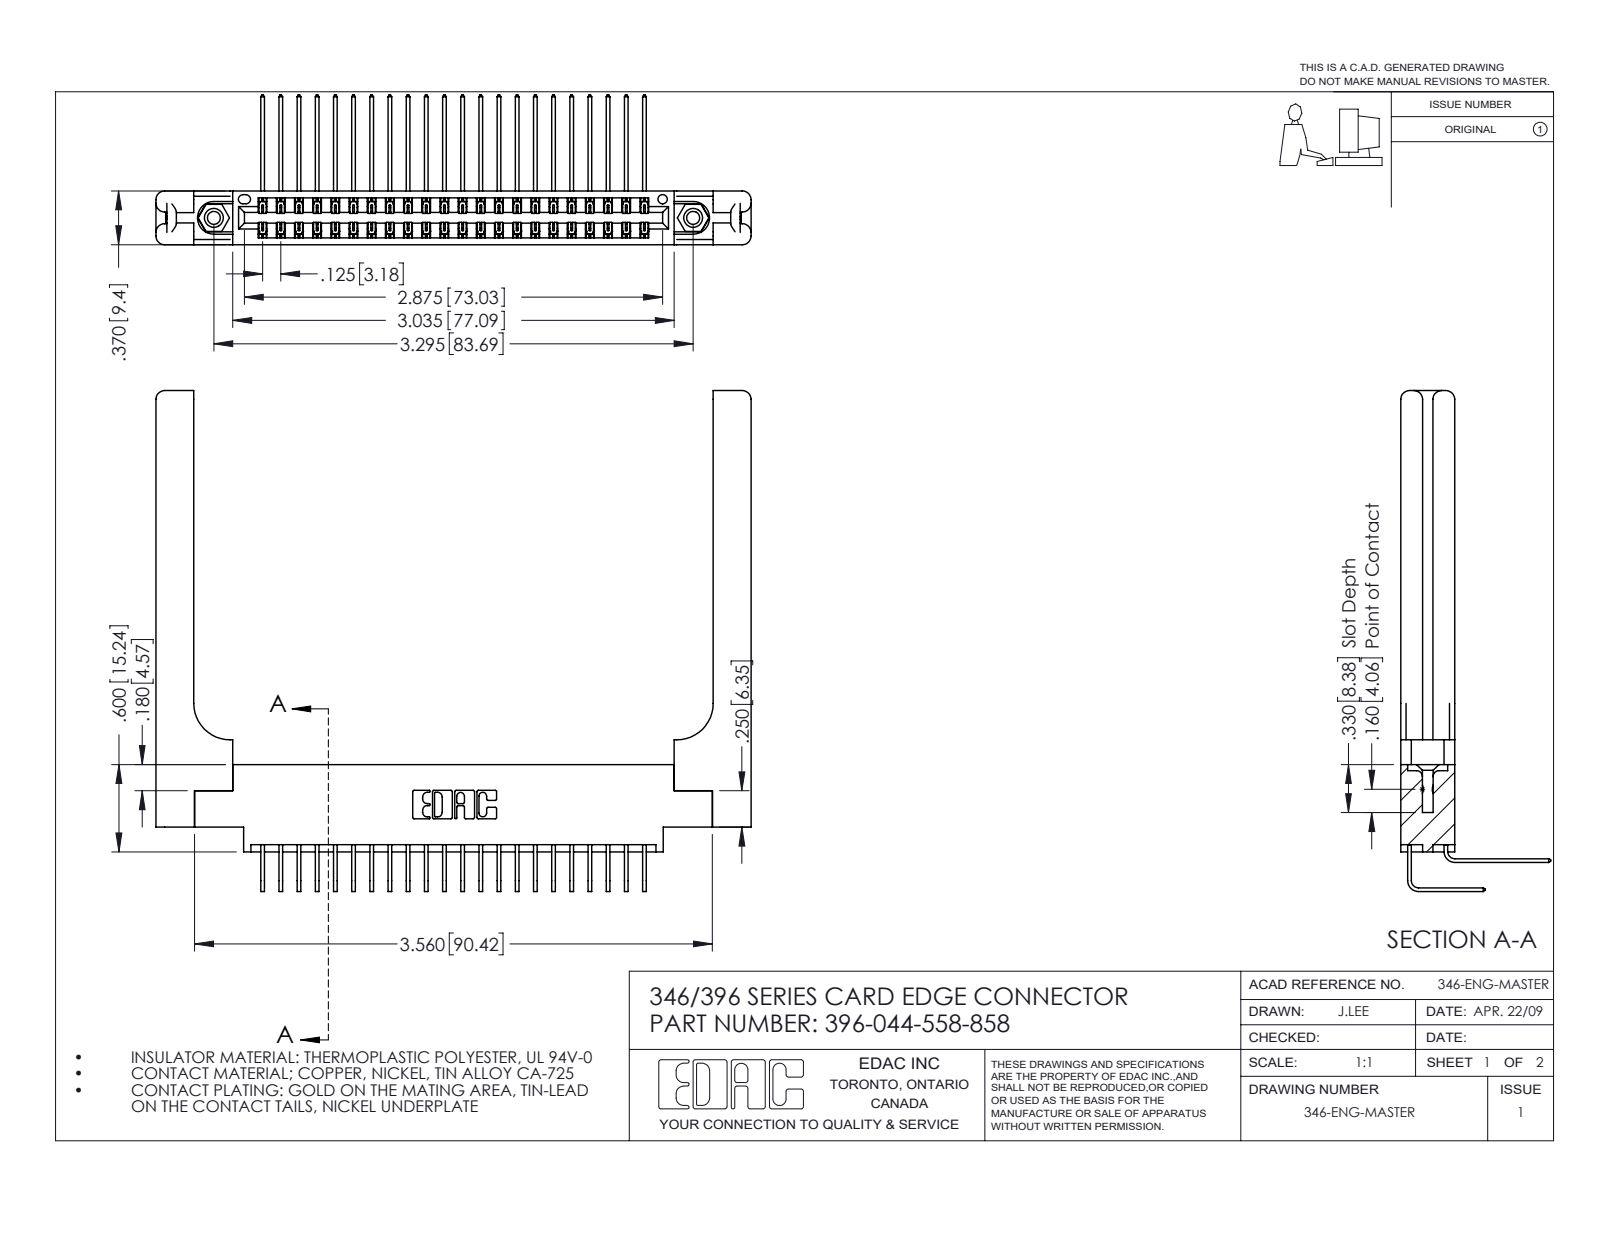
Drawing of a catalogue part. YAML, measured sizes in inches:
part_name: "396-044-558-858; 346 Part_0.170 Offset - 0.156 Dia-TH; 345-292-001_558 Tail - 2; 345-250-001_345-250-001-102 (+2 more)"
step_written_by: "SolidWorks 2016 (CONFIG_CONTROL_DESIGN)"
units: inches
bodies: {solids: 49, faces: 2758, planar: 1856, cylindrical: 842, other: 60}
overall_size: [4.091, 3.443, 1.03]
volume: 1.072
surface_area: 30.86
round_holes:
  - {diameter: 0.089, count: 2}
  - {diameter: 0.125, count: 2}
  - {diameter: 0.156, count: 2}
  - {diameter: 0.064, count: 1}
round_bosses_or_shafts:
  - {diameter: 0.155, count: 2}
partial_cylinders:
  - {radius: 0.006, count: 66}
  - {radius: 0.01, count: 22}
  - {radius: 0.06, count: 16}
  - {radius: 0.007, count: 6}
  - {radius: 0.031, count: 6}
  - {radius: 0.026, count: 3}
  - {radius: 0.014, count: 2}
  - {radius: 0.022, count: 2}
face_to_face_distances: [0.37, 0.072, 0.322, 0.048, 0.148, 0.15, 0.025, 0.25, 0.298, 0.077]
hole_center_spacings: [0.246, 3.087, 3.295]
